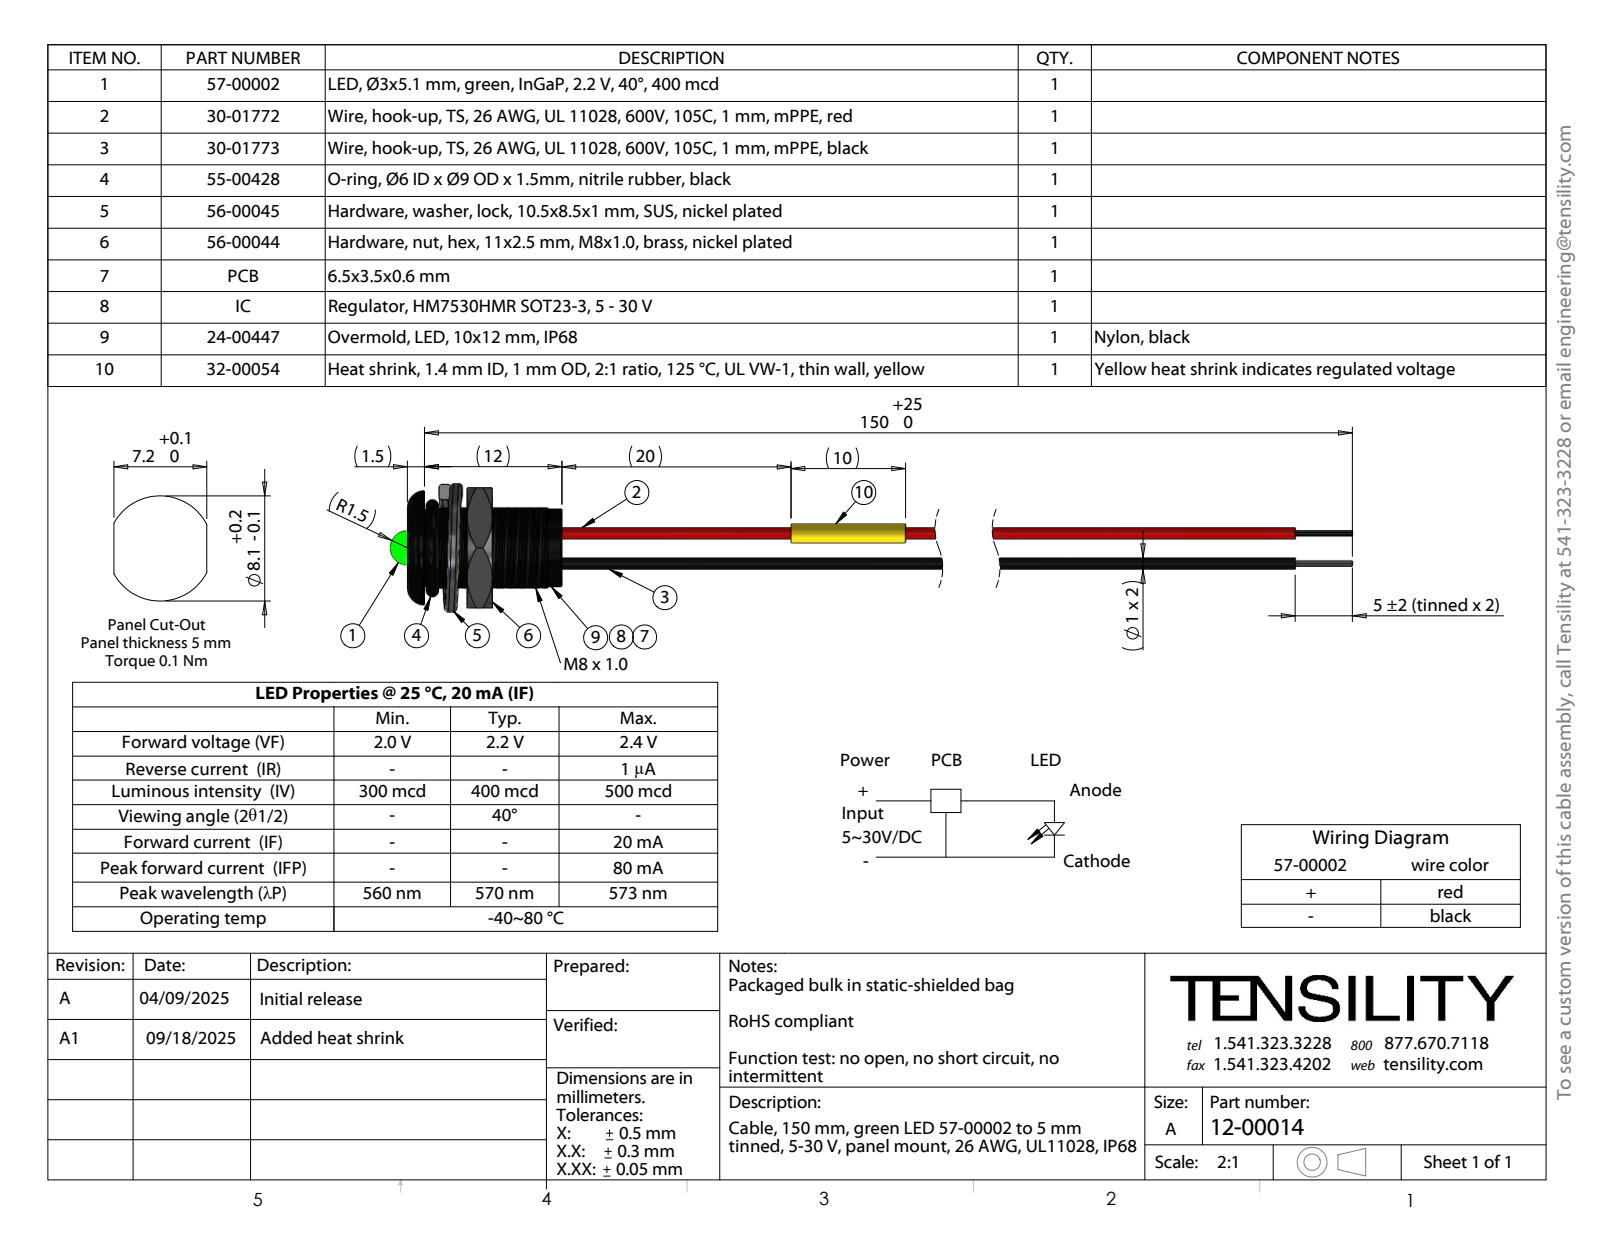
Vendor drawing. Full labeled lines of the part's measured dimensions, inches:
Part name (STEP PRODUCT): 24-00447; 57-00002_trimmed leads; 30-01773_stripped and tinned; 30-01772_stripped and tinned (+4 more)
STEP written by: SolidWorks 2021 (CONFIG_CONTROL_DESIGN)
Units: inches
Bodies: 57 solids, 555 faces (186 planar, 246 cylindrical, 123 other)
Overall size (bounding box): 6.693 × 0.477 × 0.441
Volume: 0.061 in³ · Surface area: 9.157 in²
Round holes (diameter × count): ⌀0.039 ×2
Round bosses / shafts (diameter × count): ⌀0.039 ×2, ⌀0.02 ×2, ⌀0.268 ×1, ⌀0.118 ×1
Partial cylindrical surfaces — rounded edges, fillets, slot ends (radius × count): R0.137 ×1, R0.157 ×1
Main face-to-face distances: 0.059, 0.531, 0.472, 0.413, 0.205, 0.146, 0.326, 0.292, 0.233, 0.087
Hole centre spacings: 0.014, 0.015, 0.013, 0.098, 0.099, 0.096, 0.096, 0.101
